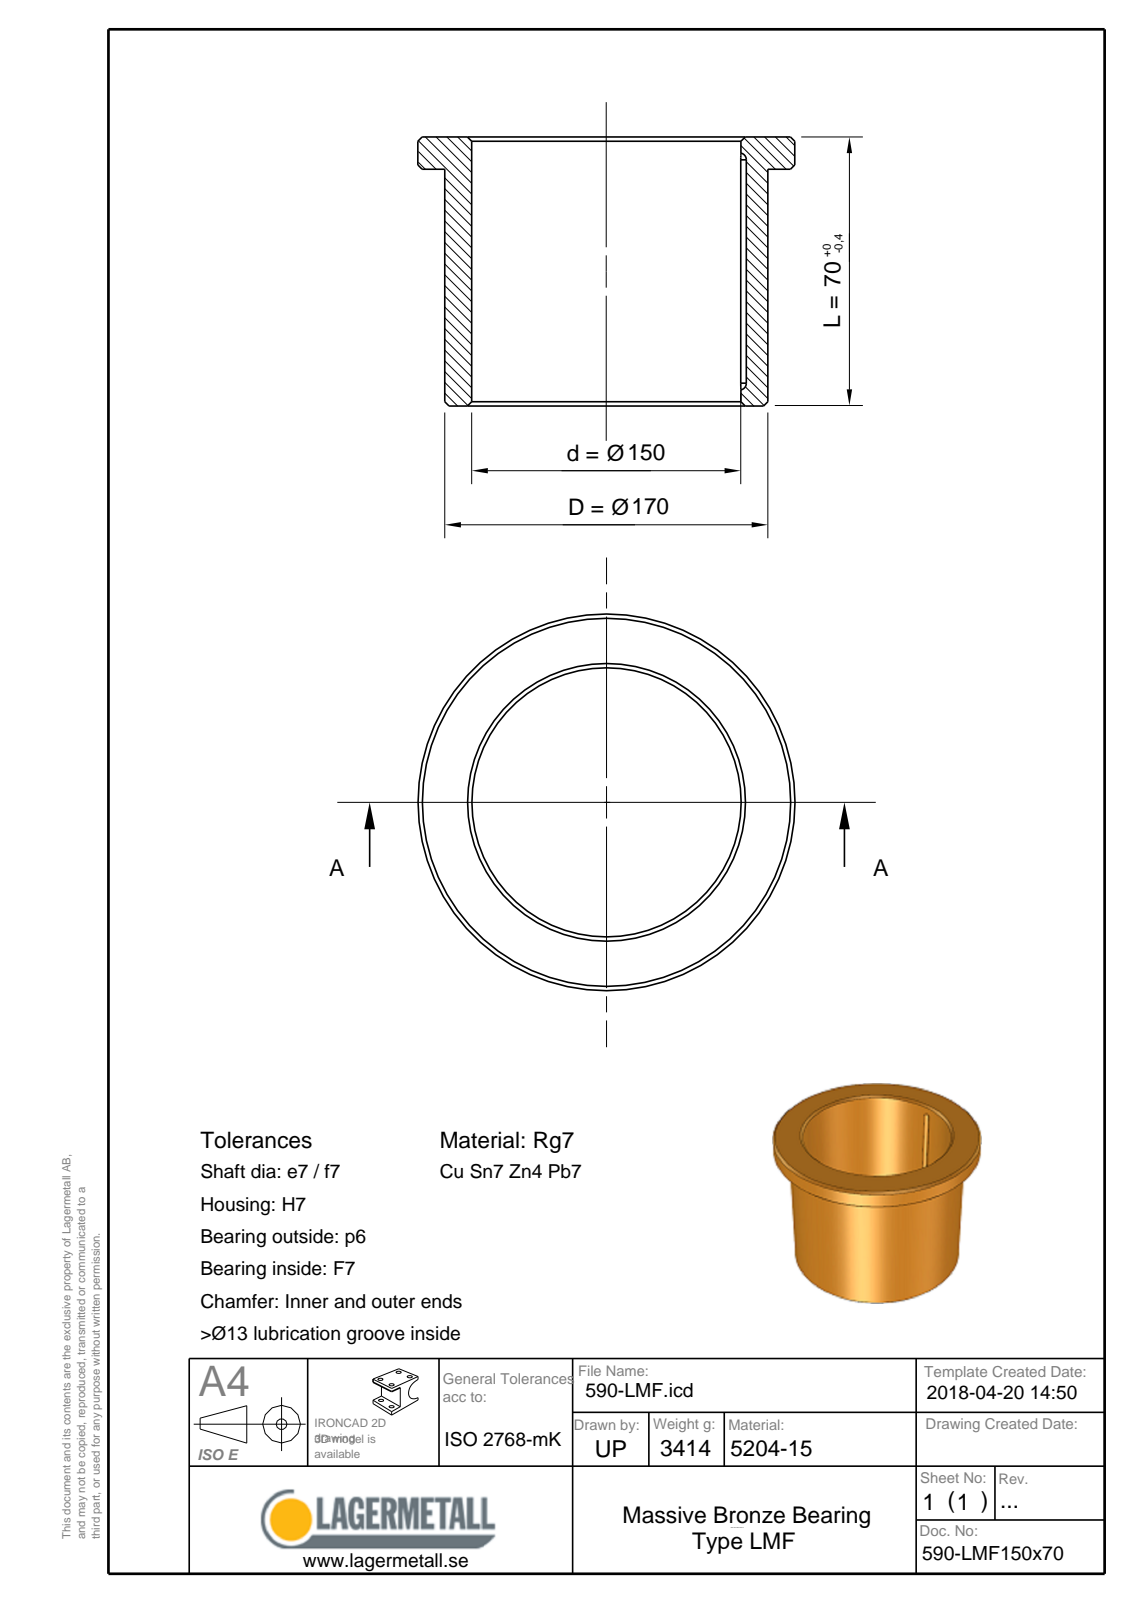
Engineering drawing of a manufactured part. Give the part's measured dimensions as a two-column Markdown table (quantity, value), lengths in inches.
| quantity | value |
| --- | --- |
| part name | 590-LMF150x70 |
| STEP written by | Spatial InterOp 3D (CONFIG_CONTROL_DESIGN) |
| units | inches |
| bodies | 1 solid, 16 faces (4 planar, 5 cylindrical, 7 other) |
| overall size | 7.283 × 7.283 × 2.756 |
| volume | 23.68 in³ |
| surface area | 133.8 in² |
| round holes (diameter × count) | 5.906 × 1 |
| round bosses / shafts (diameter × count) | 7.283 × 1, 6.693 × 1 |
| partial cylindrical surfaces (radius × count) | 0.089 × 2 |
| main face-to-face distances | 0.394, 2.362, 2.756 |
